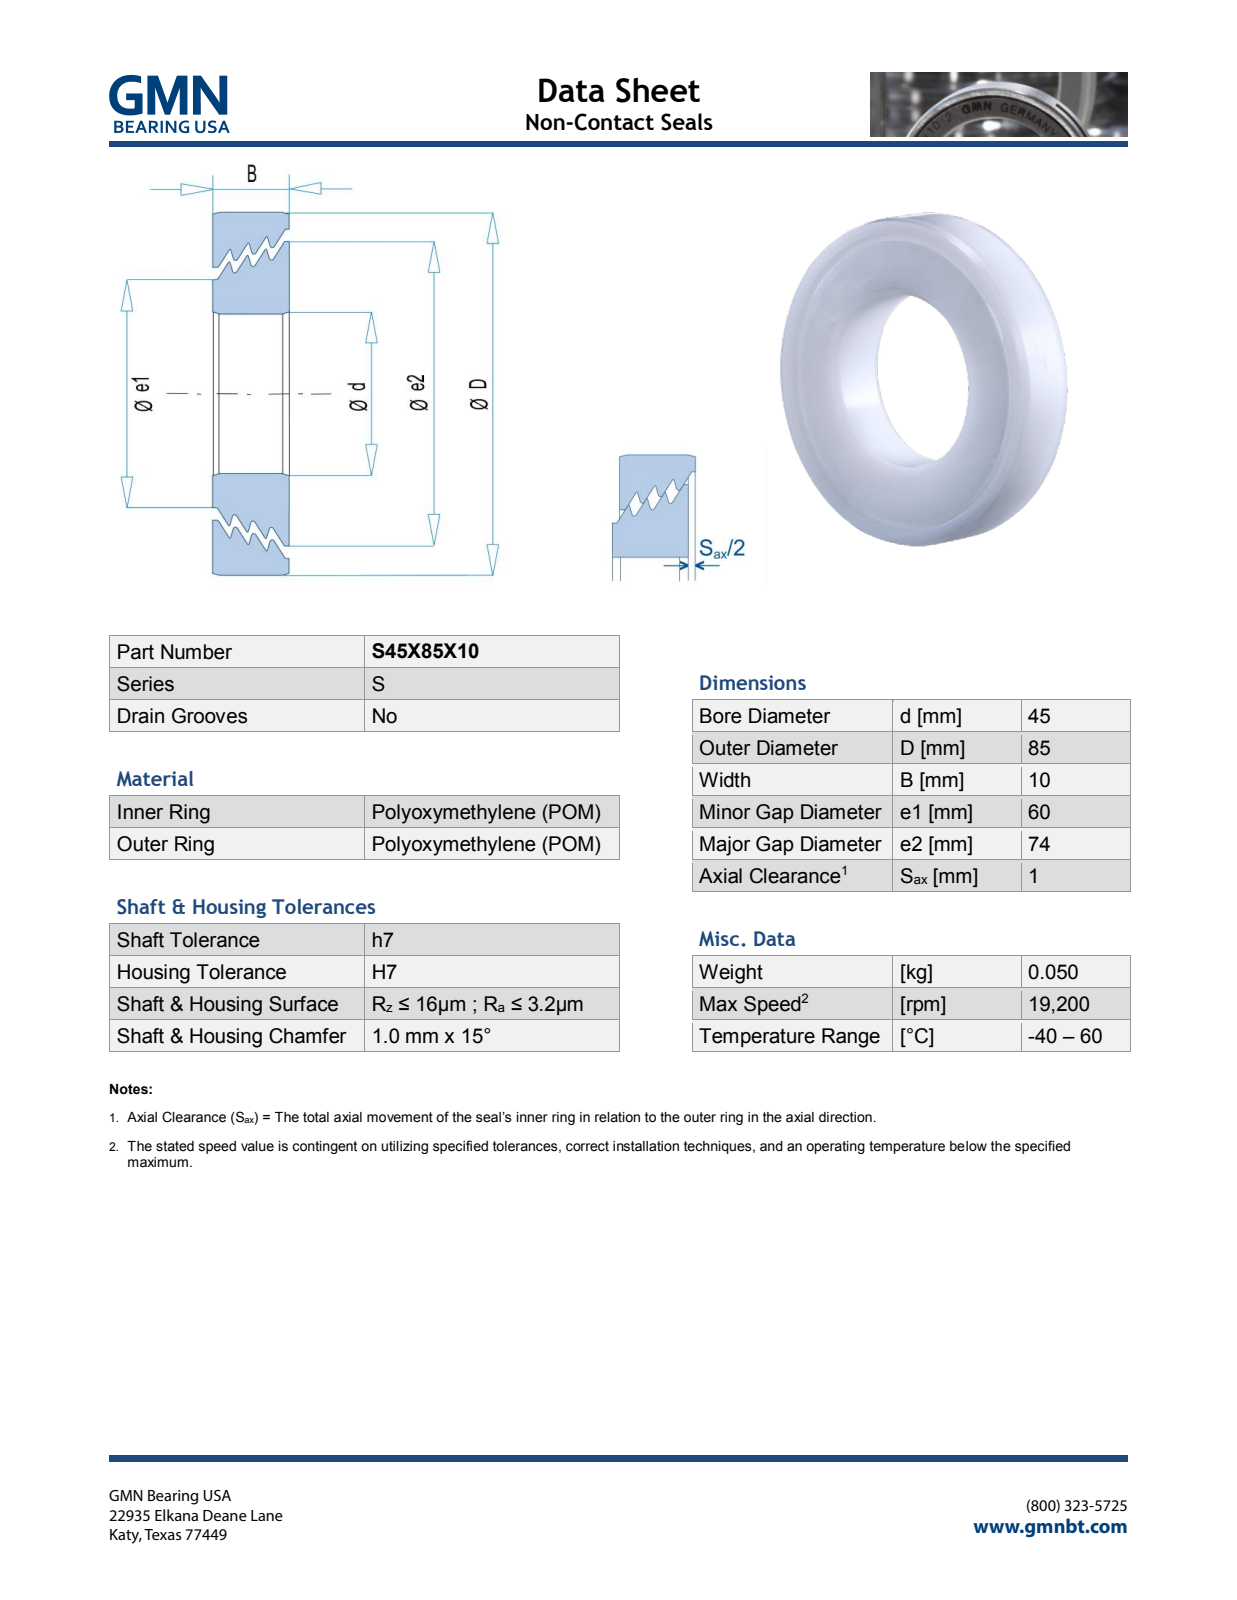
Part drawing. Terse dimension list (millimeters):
name: S45X85X10_PRT
written by: PRO/ENGINEER BY PARAMETRIC TECHNOLOGY CORPORATION, 2013150 (AUTOMOTIVE_DESIGN)
unit: mm
bodies: 2 solids, 660 faces (580 planar, 12 cylindrical, 68 other)
size: 85 × 85 × 10.07
volume: 39 001 mm³; area: 20 253 mm²
holes: 1× ⌀45, 1× ⌀61.63, 1× ⌀75.63
bosses: 1× ⌀85, 1× ⌀74, 1× ⌀60
face distances: 10, 10.07, 0.51, 4.08, 3.57, 0.52, 2.89, 0.43, 3.56, 3.06
